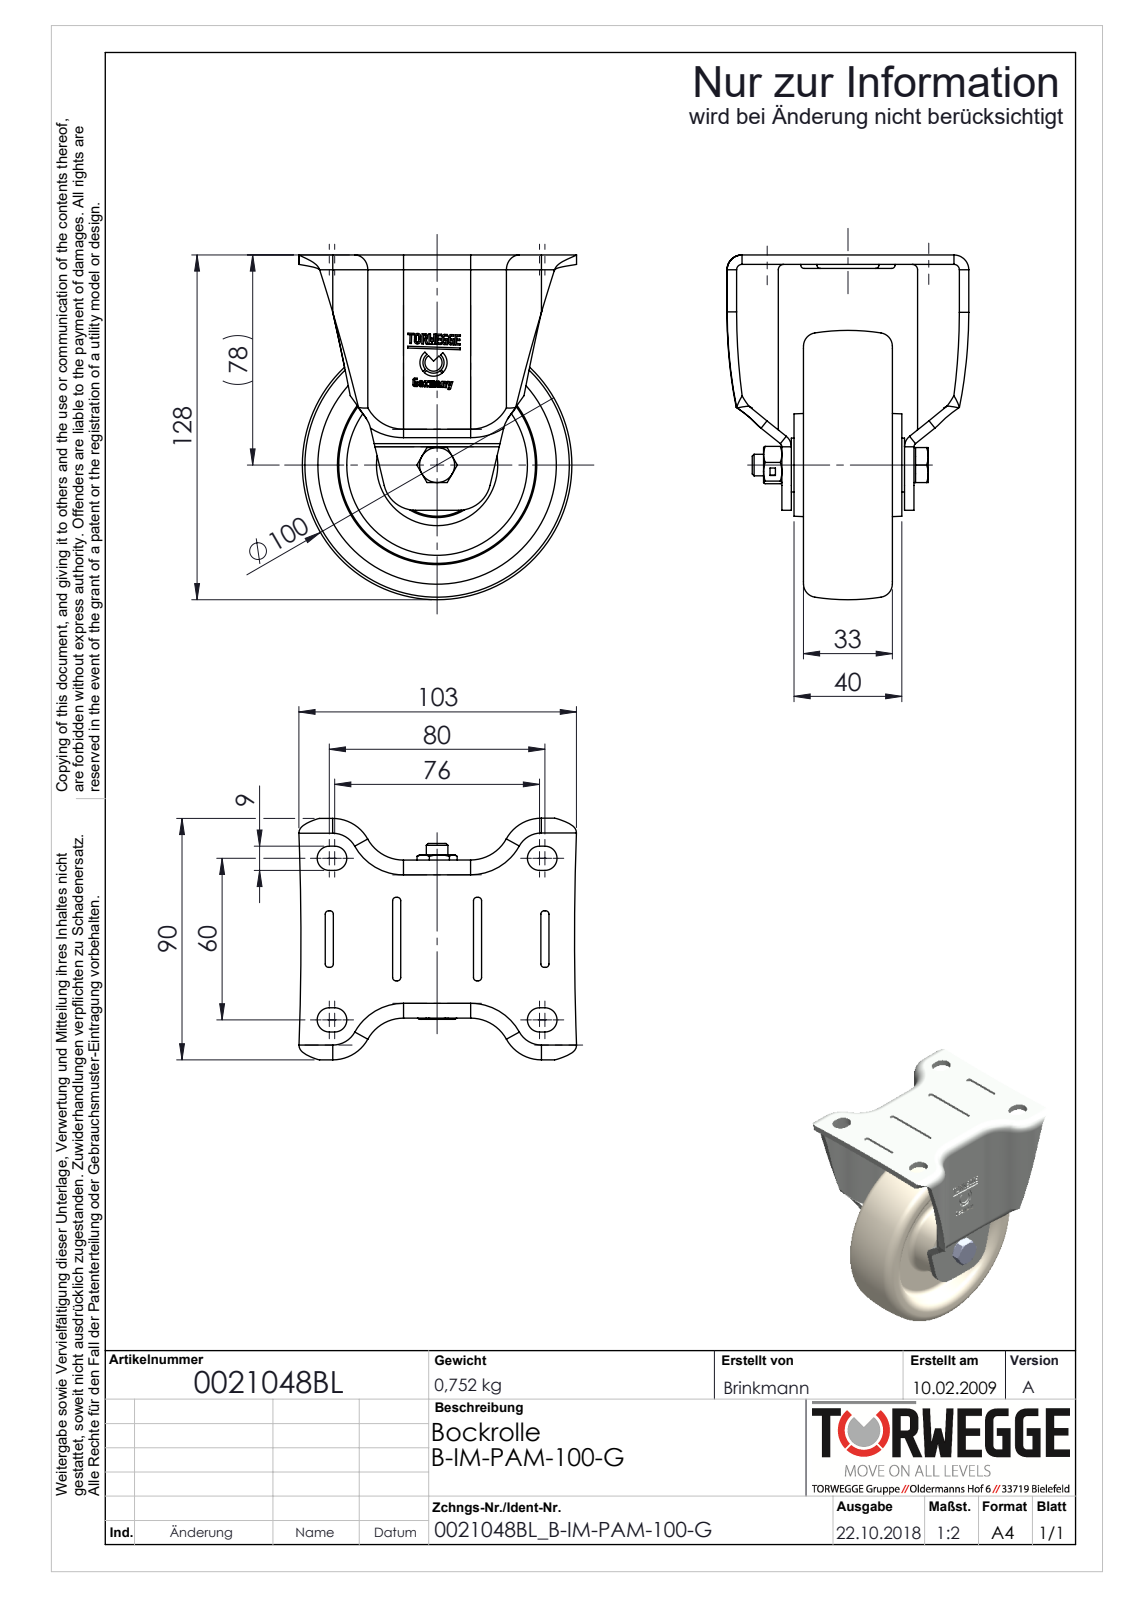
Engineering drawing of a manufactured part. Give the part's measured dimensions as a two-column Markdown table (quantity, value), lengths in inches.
| quantity | value |
| --- | --- |
| part name | 0021048BL_B-IM-PAM-100-G_(A-01) |
| STEP written by | SolidWorks 2018 (AUTOMOTIVE_DESIGN) |
| units | inches |
| bodies | 7 solids, 332 faces (96 planar, 102 cylindrical, 134 other) |
| overall size | 5.042 × 4.016 × 3.543 |
| volume | 16.09 in³ |
| surface area | 137.4 in² |
| round holes (diameter × count) | 0.268 × 1, 0.315 × 1, 0.335 × 1, 0.339 × 1, 0.472 × 1, 0.906 × 1 |
| round bosses / shafts (diameter × count) | 1.102 × 1, 0.512 × 1 |
| partial cylindrical surfaces (radius × count) | 0.118 × 16, 0.177 × 12, 0.472 × 12, 0.335 × 6, 0.039 × 4, 0.394 × 4, 0.531 × 4, 0.61 × 4 |
| main face-to-face distances | 0.138, 0.984, 0.197, 1.988, 0.725, 1.161, 1.299, 0.61, 0.807, 2.598 |
